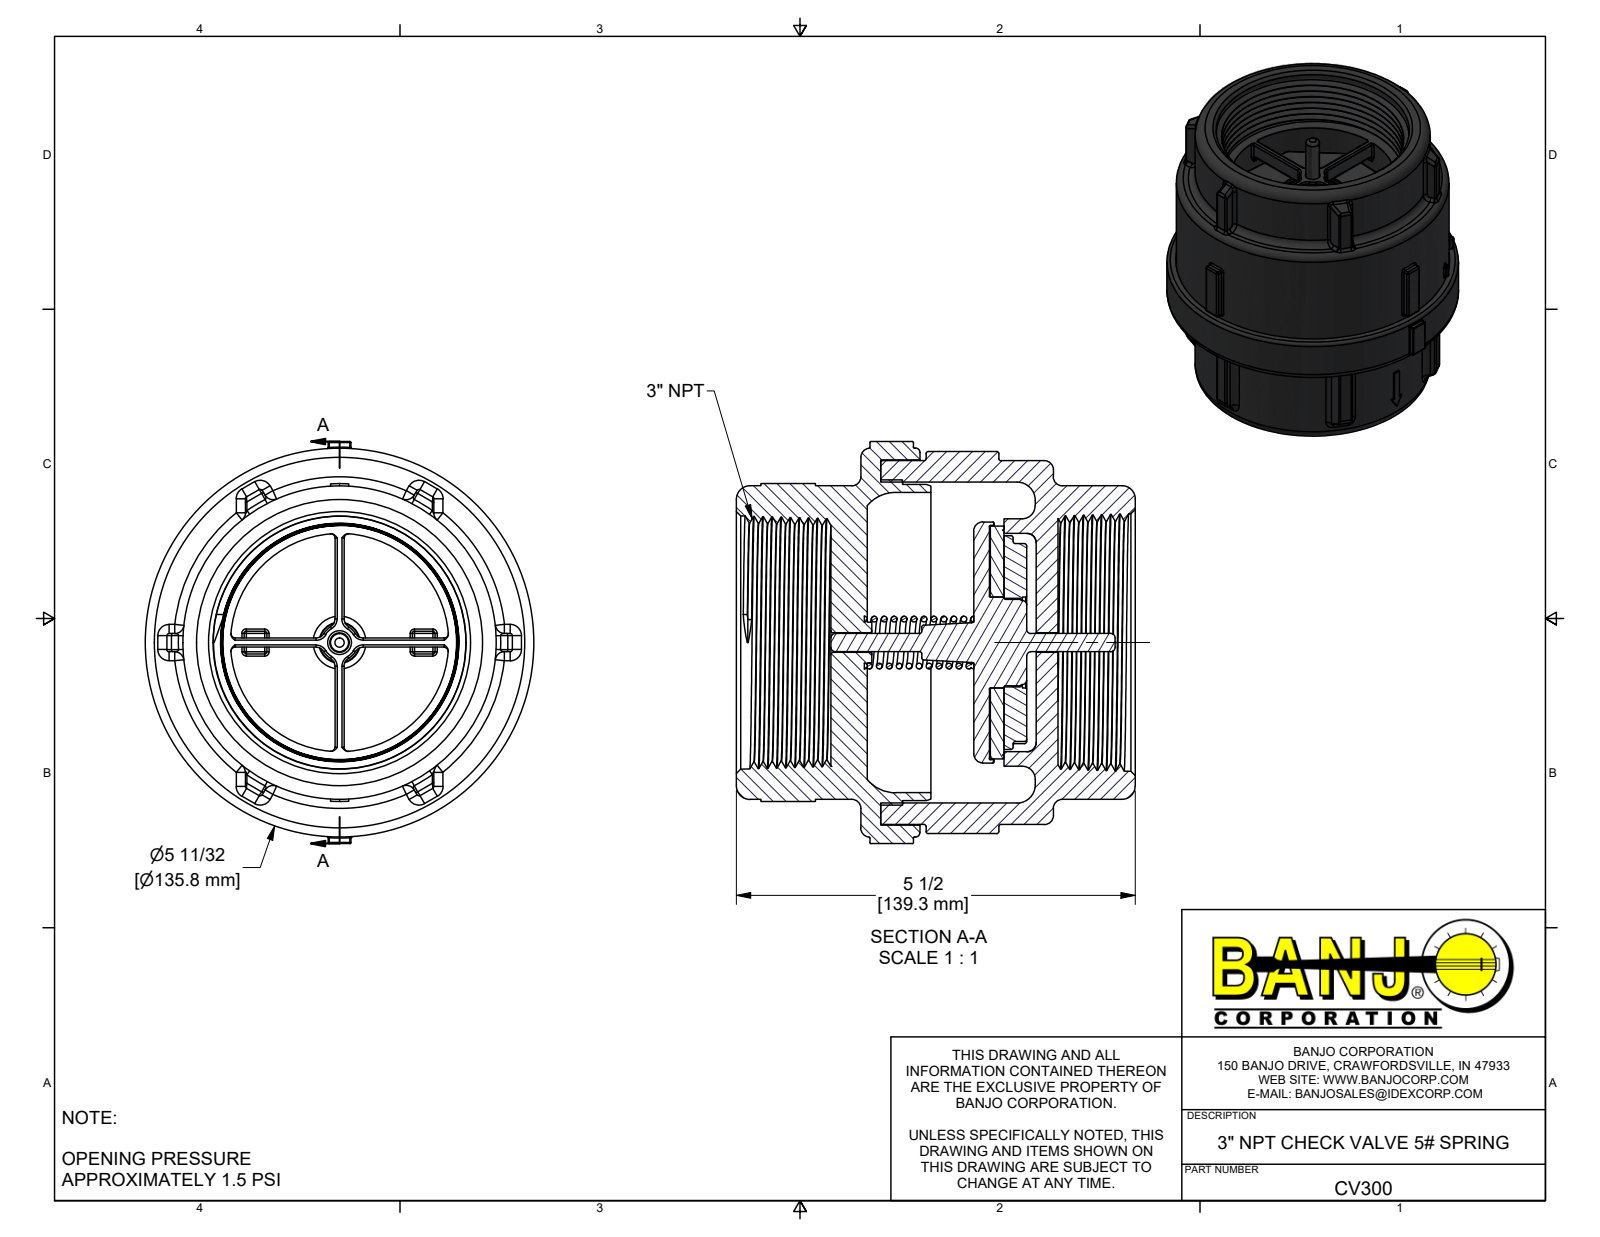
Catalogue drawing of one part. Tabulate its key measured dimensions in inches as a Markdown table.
| quantity | value |
| --- | --- |
| part name | CV300; CV30054; CV30054X; CV30056 (+6 more) |
| STEP written by | Autodesk Inventor 2022 (AUTOMOTIVE_DESIGN) |
| units | inches |
| bodies | 6 solids, 1039 faces (177 planar, 320 cylindrical, 542 other) |
| overall size | 5.525 × 5.484 × 5.345 |
| volume | 43.04 in³ |
| surface area | 330.1 in² |
| round holes (diameter × count) | 0.27 × 1, 1.189 × 1, 1.25 × 1, 3 × 1, 3.22 × 1, 4.125 × 1, 4.41 × 1, 5.02 × 1 |
| round bosses / shafts (diameter × count) | 5.345 × 1, 5 × 1, 4.47 × 1, 4.35 × 1, 4.345 × 1, 4.31 × 1, 3.4 × 1, 3.313 × 1 |
| partial cylindrical surfaces (radius × count) | 0.03 × 125, 0.06 × 36, 0.125 × 34, 0.015 × 16, 0.25 × 1, 0.28 × 1, 0.982 × 1, 2.185 × 1 |
| main face-to-face distances | 1.695, 0.187, 1.28, 0.415, 0.228, 1.507, 0.313, 0.2, 0.013, 0.215 |
